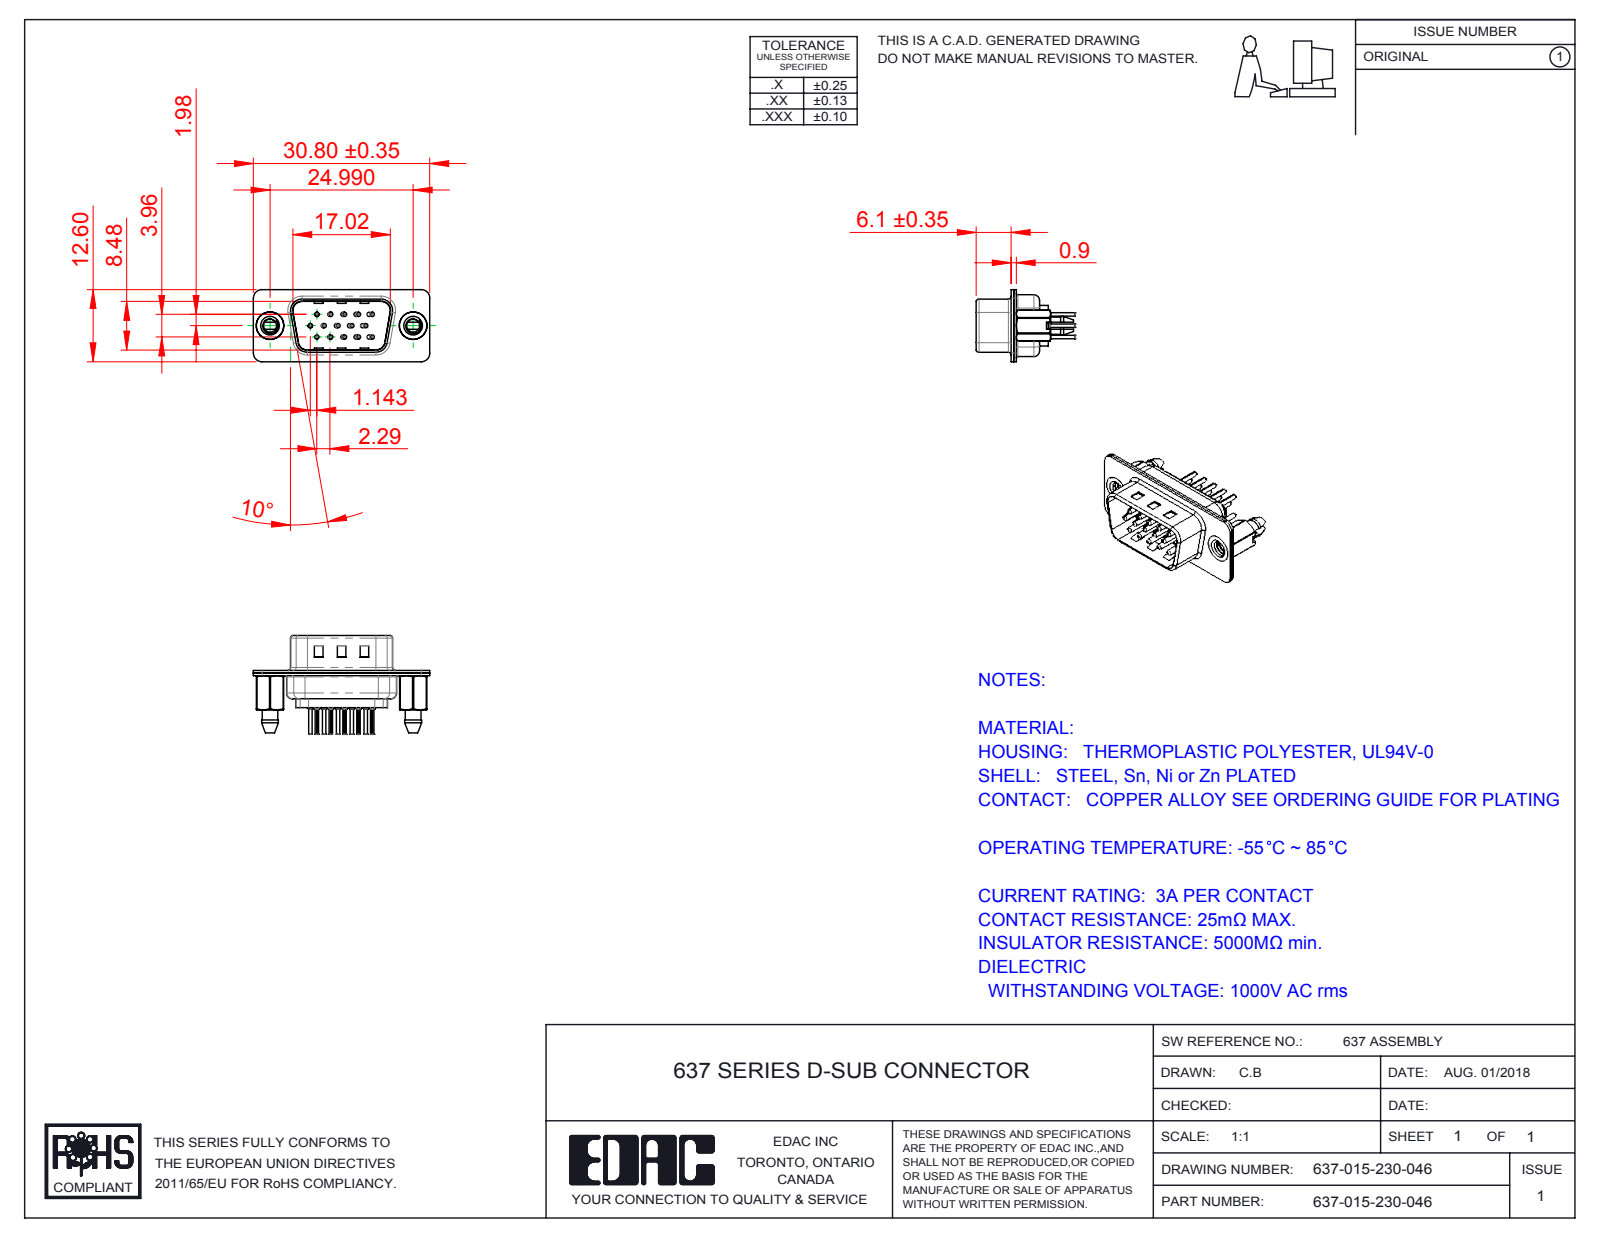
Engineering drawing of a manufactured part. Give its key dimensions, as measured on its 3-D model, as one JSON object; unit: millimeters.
{"part_name": "637 Contact Row 3_30; 637 Shell Front_15 Contacts; 637 Contact Row 2_30; 637 Housing_15 Contacts (+4 more)", "step_written_by": "SolidWorks 2016 (CONFIG_CONTROL_DESIGN)", "units": "millimeters", "bodies": {"solids": 20, "faces": 1878, "planar": 499, "cylindrical": 716, "other": 663}, "overall_size": [30.8, 17.25, 12.6], "volume_mm3": 1429, "surface_area_mm2": 4933, "round_holes": [[1.6, 27], [0.2, 15], [0.35, 15], [1.1, 15], [0.75, 12], [2, 12], [2.26, 2], [4, 2], [4.8, 2]], "round_bosses_or_shafts": [[2, 15], [1.5, 15], [0.75, 15], [0.6, 15], [4.9, 2]], "partial_cylinders_radius": [[0.1, 30], [1.5, 18], [2, 12], [0.5, 8], [1.6, 6], [0.25, 4], [0.55, 4], [0.7, 4]], "face_to_face_distances": [0.45, 0.4, 0.9, 8.48, 0.7, 8.88, 6.5, 4.55, 0.31, 1.05], "hole_center_spacings": [3.96, 2.29, 2.28, 4.57, 2.42, 6.05, 4.84, 2.35]}
